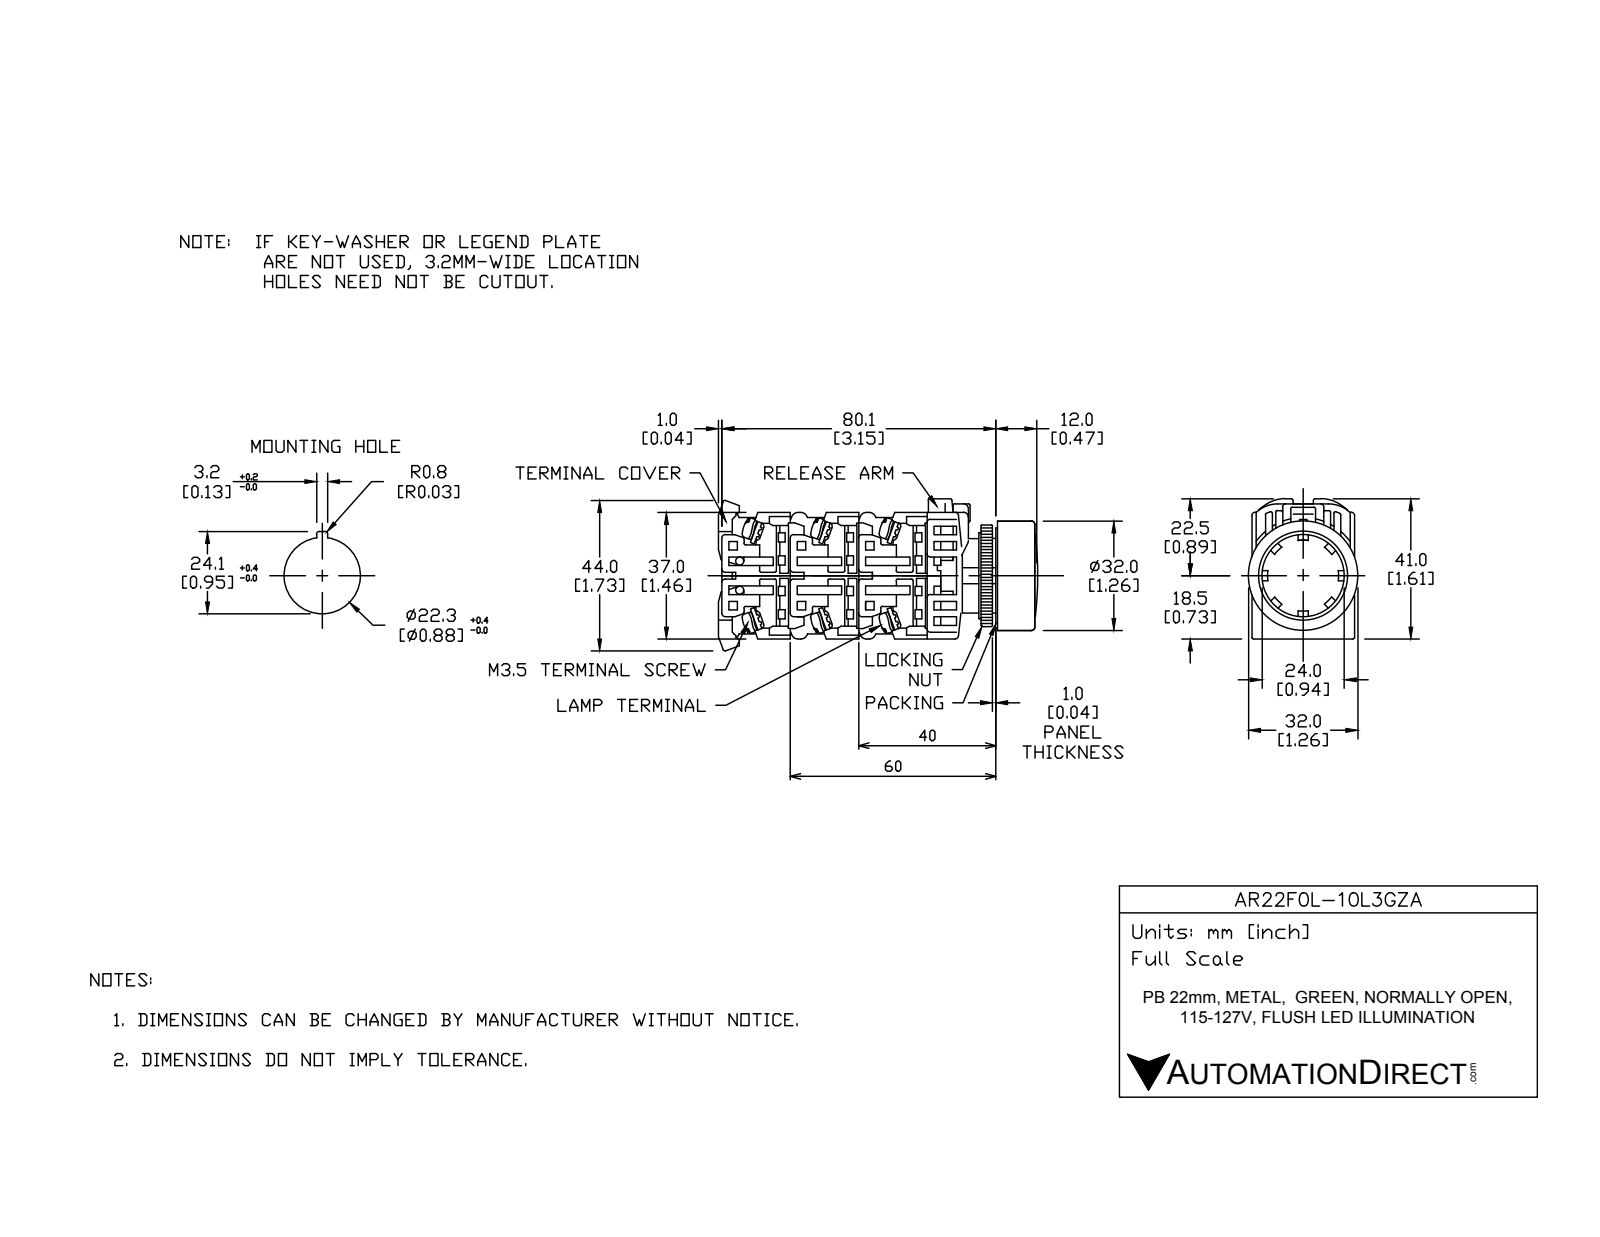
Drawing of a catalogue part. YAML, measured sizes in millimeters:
part_name: "AR22F0L-10L3GZA"
step_written_by: "SolidWorks 2017 (AUTOMOTIVE_DESIGN)"
units: millimeters
bodies: {solids: 16, faces: 451, planar: 317, cylindrical: 99, other: 35}
overall_size: [72.75, 43.81, 32]
volume: 47521
surface_area: 25721
round_holes:
  - {diameter: 21.8, count: 1}
  - {diameter: 22, count: 1}
  - {diameter: 25, count: 1}
  - {diameter: 31, count: 1}
round_bosses_or_shafts:
  - {diameter: 5, count: 4}
  - {diameter: 32, count: 1}
  - {diameter: 30.5, count: 1}
  - {diameter: 29.8, count: 1}
  - {diameter: 24, count: 1}
  - {diameter: 23.8, count: 1}
  - {diameter: 21.75, count: 1}
  - {diameter: 17, count: 1}
partial_cylinders:
  - {radius: 0.5, count: 32}
  - {radius: 1.75, count: 8}
  - {radius: 5, count: 4}
  - {radius: 4, count: 2}
  - {radius: 16.59, count: 1}
  - {radius: 17.59, count: 1}
face_to_face_distances: [1, 18, 29, 20, 28.5, 3, 2, 21, 0.35, 7.5]
